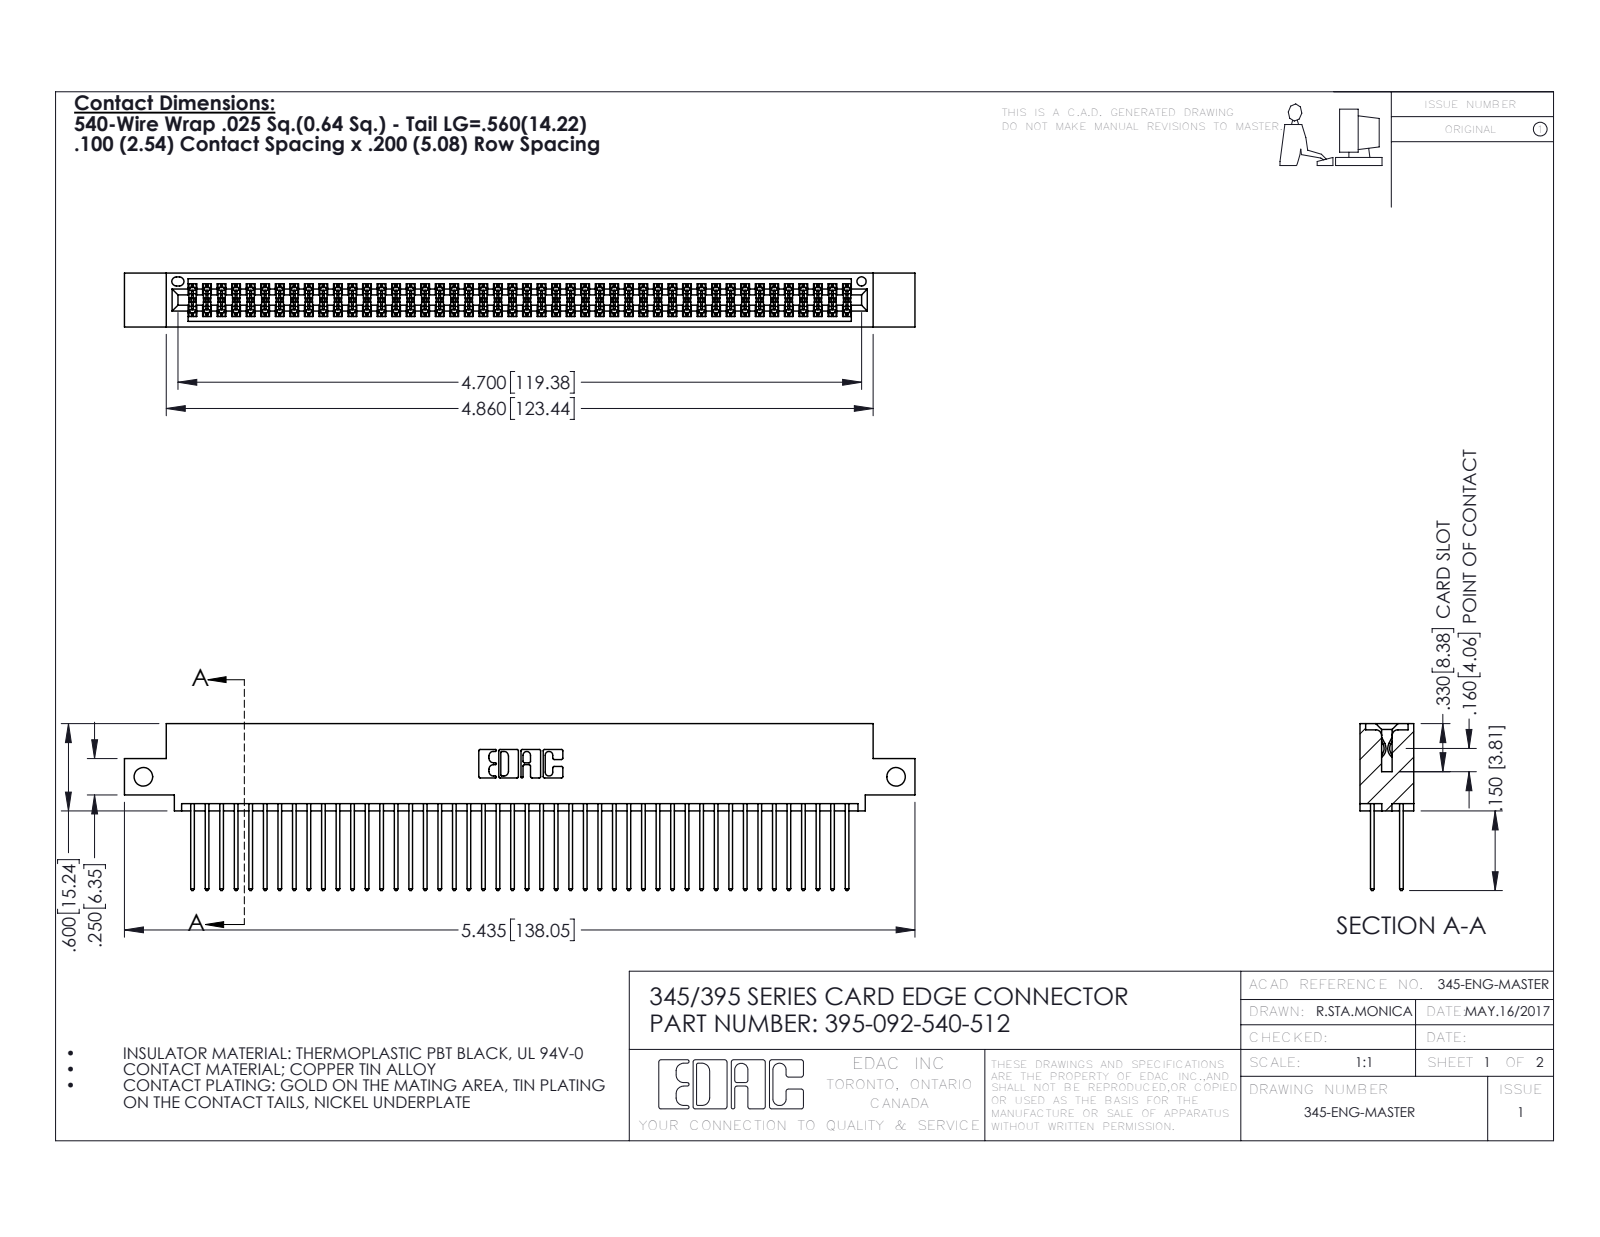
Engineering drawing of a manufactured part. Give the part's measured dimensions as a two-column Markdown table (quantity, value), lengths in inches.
| quantity | value |
| --- | --- |
| part name | 345 Part_0.110 Offset - Side Mount; 345-292-001_345-293-140; 395-092-540-512 |
| STEP written by | SolidWorks 2016 (CONFIG_CONTROL_DESIGN) |
| units | inches |
| bodies | 93 solids, 4730 faces (3120 planar, 1610 cylindrical, 0 other) |
| overall size | 5.435 × 1.147 × 0.37 |
| volume | 0.832 in³ |
| surface area | 33.8 in² |
| round holes (diameter × count) | 0.128 × 2, 0.064 × 1 |
| partial cylindrical surfaces (radius × count) | 0.006 × 138, 0.01 × 92, 0.01 × 22, 0.007 × 6, 0.031 × 6, 0.026 × 3, 0.014 × 2, 0.019 × 2 |
| main face-to-face distances | 0.298, 0.072, 0.2, 0.098, 0.272, 0.025, 0.37, 0.225, 0.175, 0.149 |
| hole center spacings | 5.175 |
